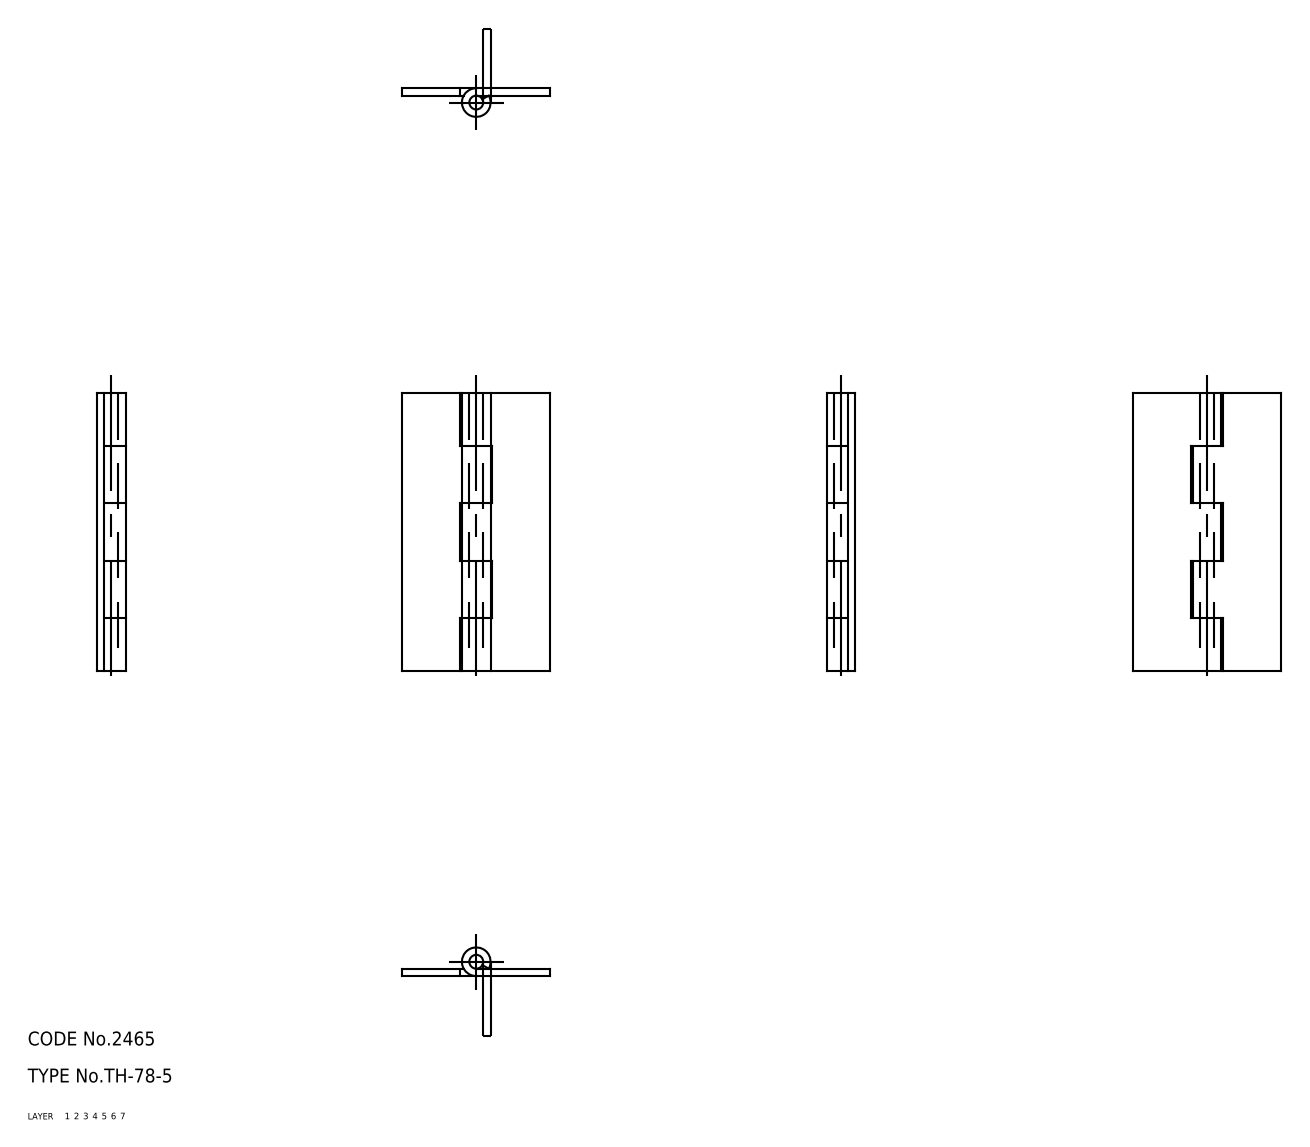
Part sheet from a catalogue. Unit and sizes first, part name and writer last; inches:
Units: inches
Overall size (bounding box): 2.362 × 1.26 × 0.244
Volume: 0.263 in³ · Surface area: 9.528 in²
Bodies: 3 solids, 42 faces (0 planar, 0 cylindrical, 42 other)
Part name (STEP PRODUCT): hinge piece_B; hinge piece_A; shaft; TH_78_5_16769_36
STEP written by: CADfix (AUTOMOTIVE_DESIGN)
